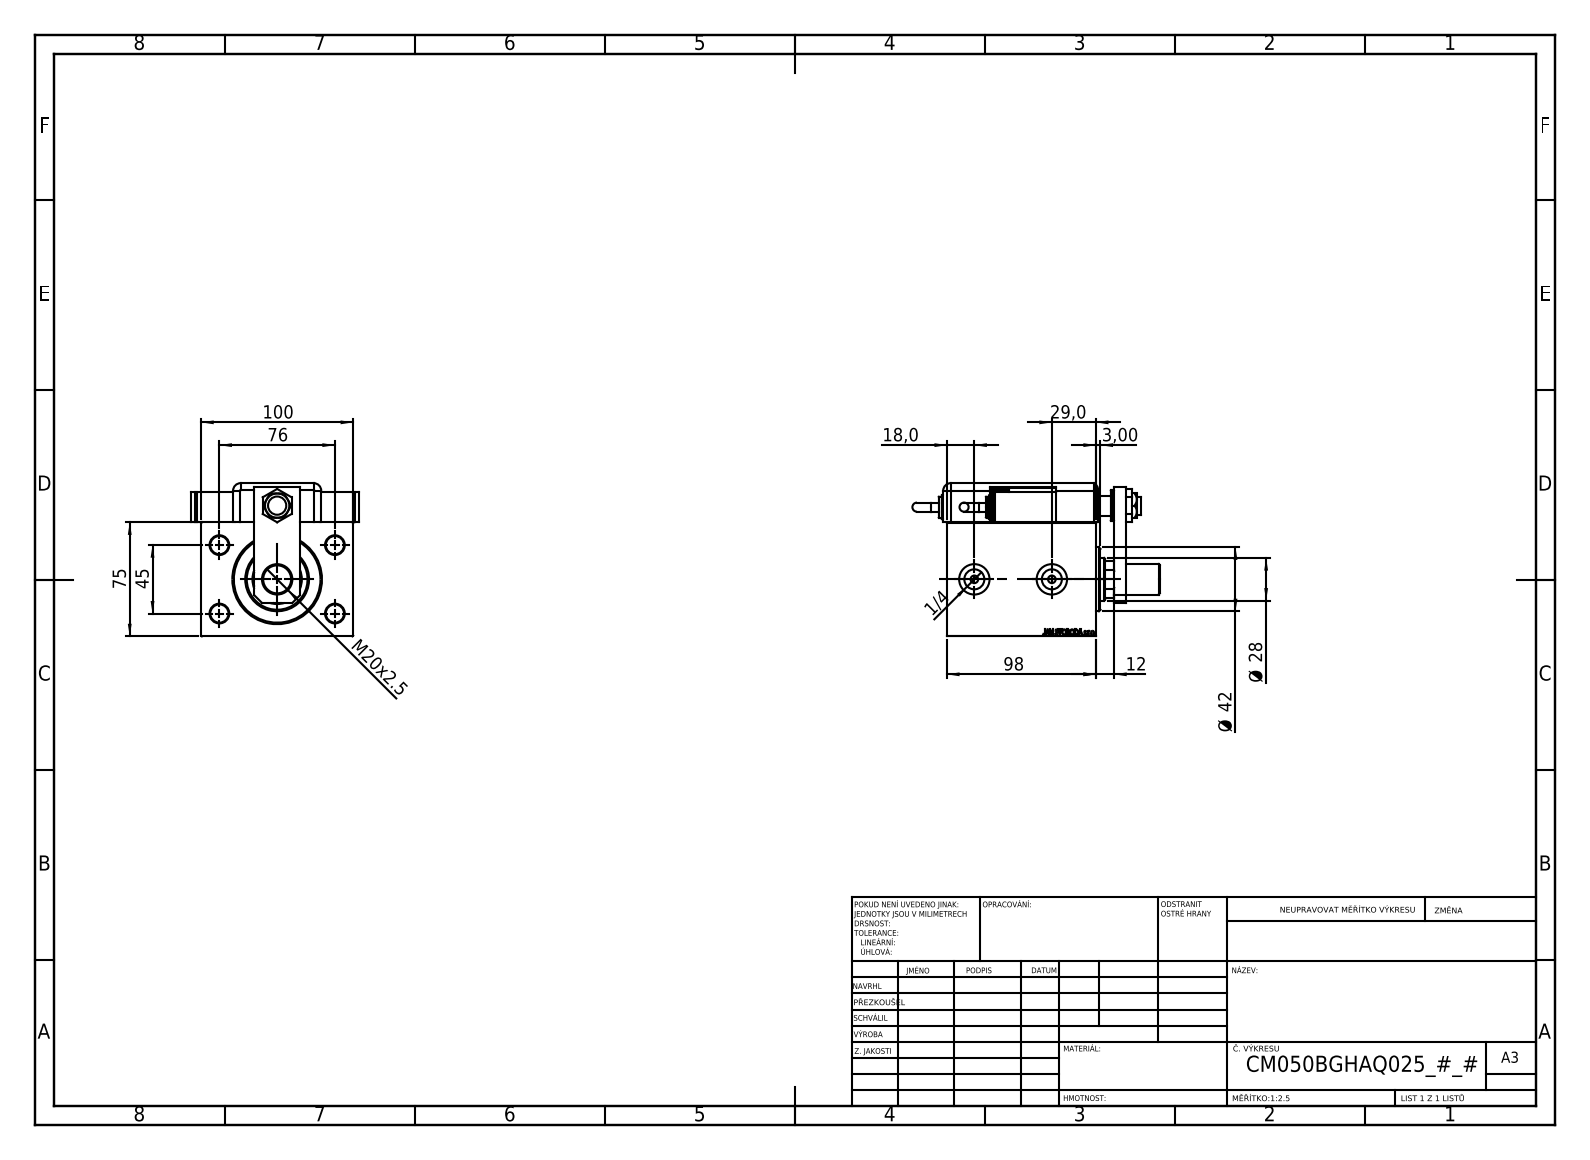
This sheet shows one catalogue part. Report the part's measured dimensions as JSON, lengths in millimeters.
{"part_name": "SWITCH DIM A_G; SWITCH Q; ZARAZKA_Q; TYC (+8 more)", "step_written_by": "SolidWorks 2019 (CONFIG_CONTROL_DESIGN)", "units": "millimeters", "bodies": {"solids": 14, "faces": 1282, "planar": 612, "cylindrical": 115, "other": 555}, "overall_size": [162.76, 111, 100.8], "volume_mm3": 830395, "surface_area_mm2": 151677, "round_holes": [[12, 5], [20, 3], [4, 2], [5, 2], [8, 2], [13.16, 2], [13, 1], [14, 1], [18.5, 1], [28, 1], [31.5, 1], [32.5, 1]], "round_bosses_or_shafts": [[20, 3], [16, 2], [14, 2], [6, 2], [42, 1], [18, 1]], "partial_cylinders_radius": [[5, 9], [10, 1], [13.5, 1]], "face_to_face_distances": [75, 3, 98, 100, 14, 20, 84, 25.8, 100.8, 13.5], "hole_center_spacings": [44.16, 45, 46.04, 76, 80.53, 88.32, 20, 48.5]}
